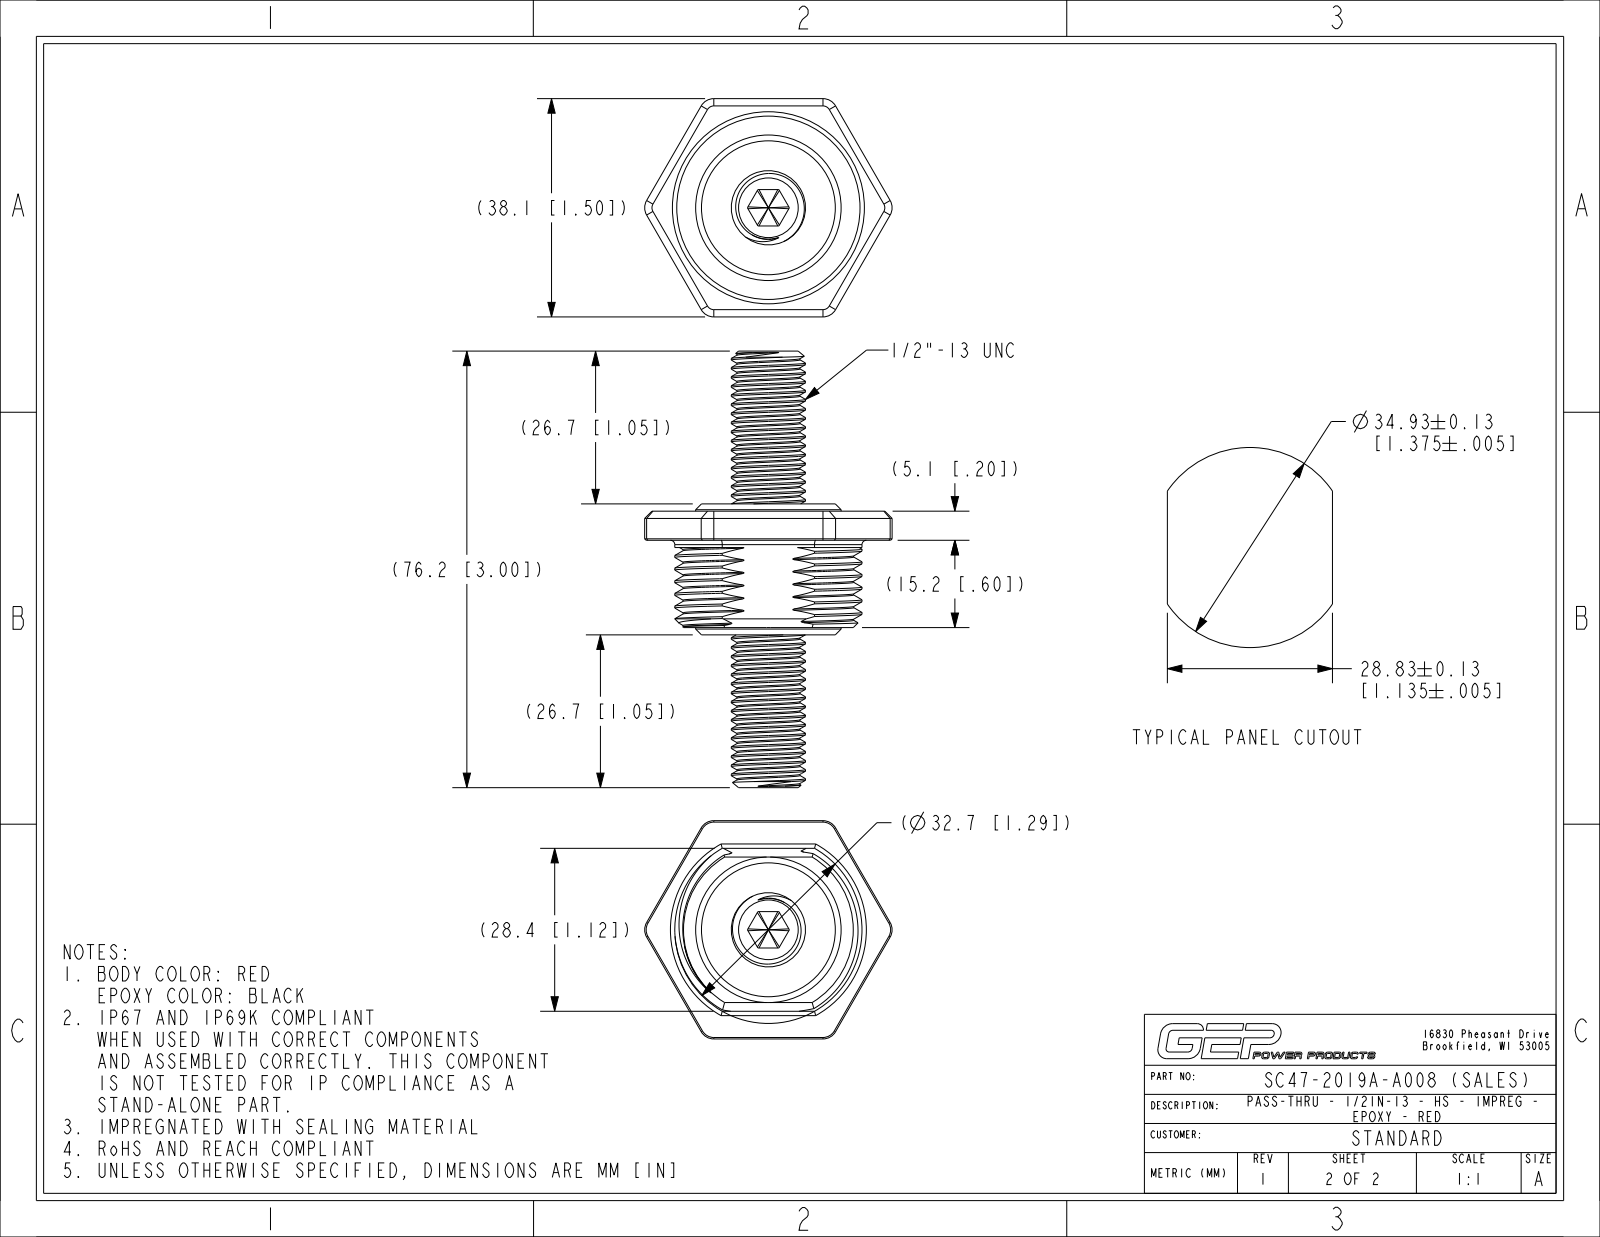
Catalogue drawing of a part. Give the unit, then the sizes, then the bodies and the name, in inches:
Units: inches
Overall size (bounding box): 3 × 1.701 × 1.5
Round holes (diameter × count): ⌀0.422 ×1, ⌀0.84 ×1, ⌀1.26 ×1
Round bosses / shafts (diameter × count): ⌀1.26 ×1, ⌀1 ×1, ⌀0.51 ×1
Partial cylindrical surfaces — rounded edges, fillets, slot ends (radius × count): R0.1 ×6, R0.181 ×6, R0.03 ×2, R0.644 ×1
Main face-to-face distances: 0.574, 0.573, 0.05, 0.25, 0.85, 0.08, 0.17, 0.65, 0.73, 0.9
Volume: 1.475 in³ · Surface area: 26.8 in²
Bodies: 5 solids, 625 faces (286 planar, 169 cylindrical, 170 other)
Part name (STEP PRODUCT): C07-1002_NCF; PC40-2005A-B008_MOLD_NCF; PC40-2005A-B008_NCF_ASM; PC05-2016A-A000_NCF (+6 more)
STEP written by: CREO PARAMETRIC BY PTC INC, 2024014 (CONFIG_CONTROL_DESIGN)
